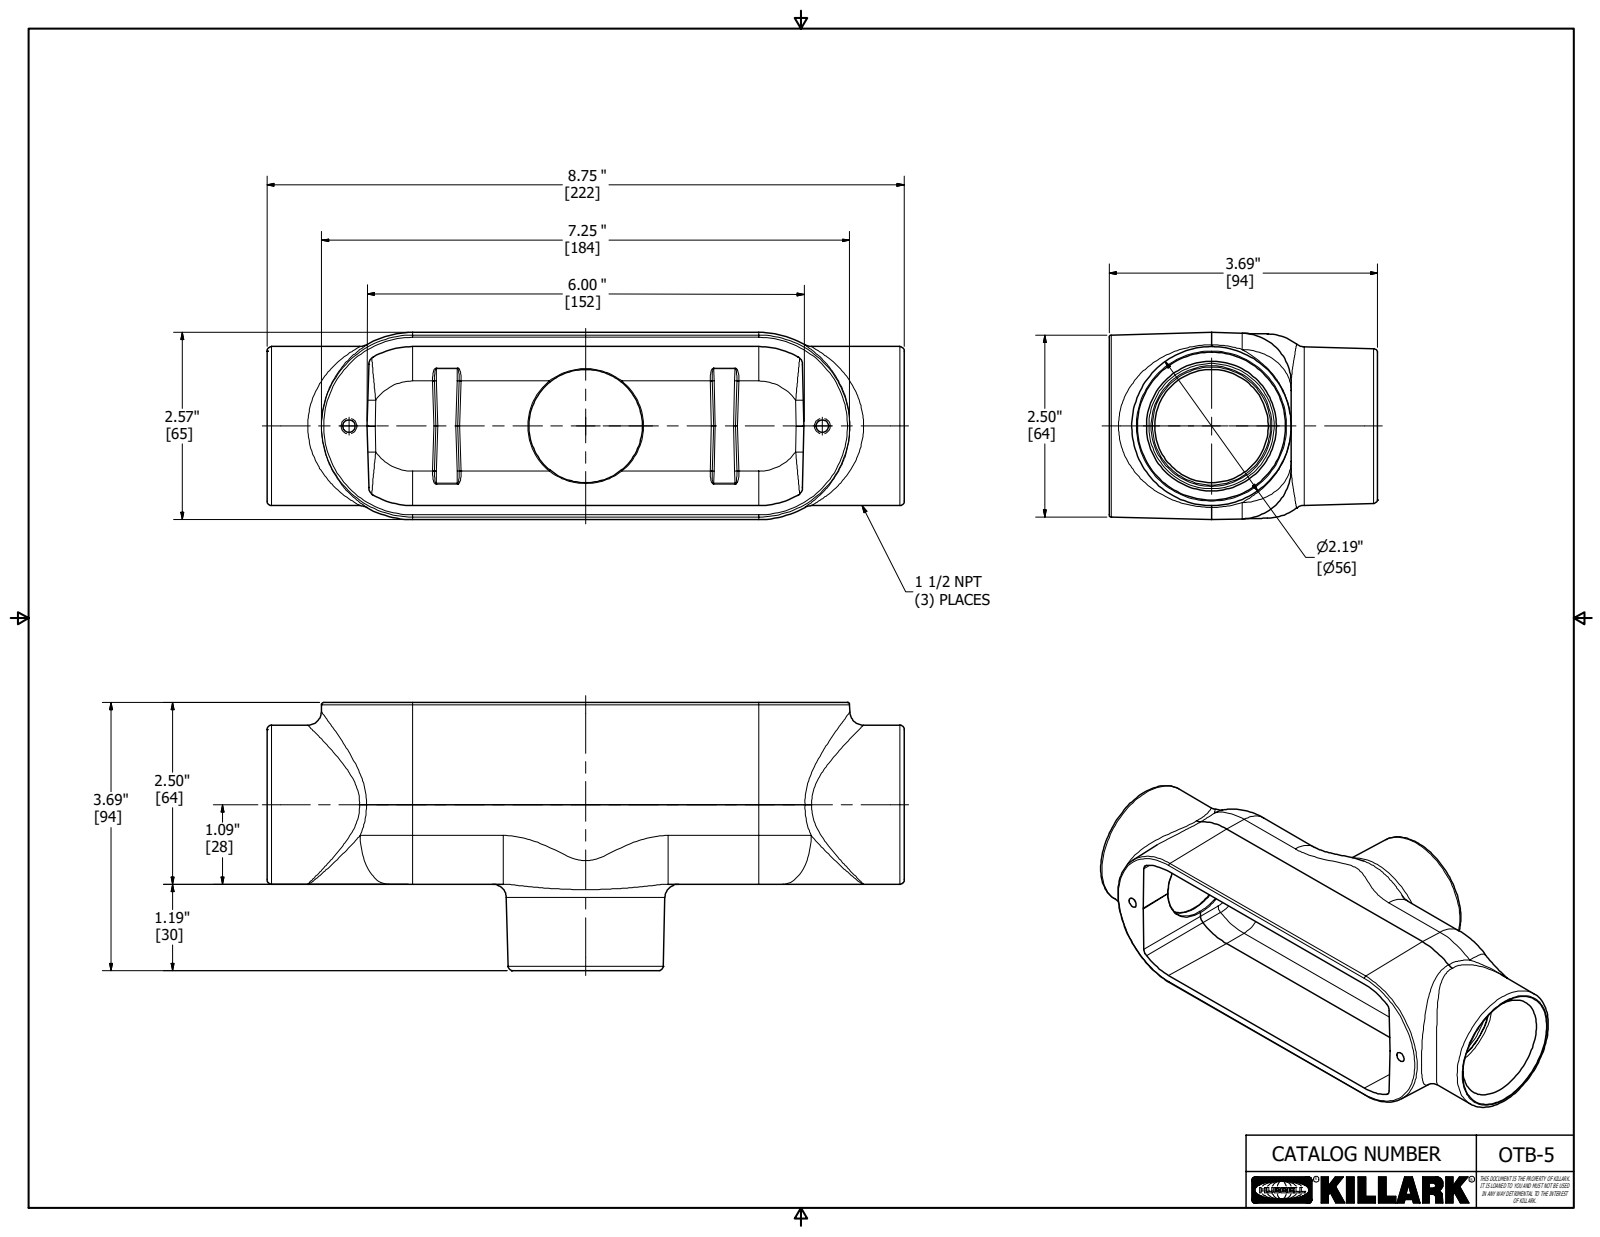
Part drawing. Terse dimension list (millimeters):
name: 13932-1
written by: Autodesk Inventor 2018 (AUTOMOTIVE_DESIGN)
unit: mm
bodies: 1 solid, 392 faces (146 planar, 73 cylindrical, 173 other)
size: 222.3 × 93.7 × 65.4
volume: 209 800 mm³; area: 88 130 mm²
holes: 2× ⌀4.3, 2× ⌀39.6
bosses: 1× ⌀55.5
rounds: 32× R0.8, 4× R3.2, 2× R6.4, 2× R12.7, 2× R17.4
face distances: 4, 61.4, 65.4, 4, 57.4, 61.4, 4.7, 63.5, 58.8, 5.6
hole spacings: 82.6, 165.1
